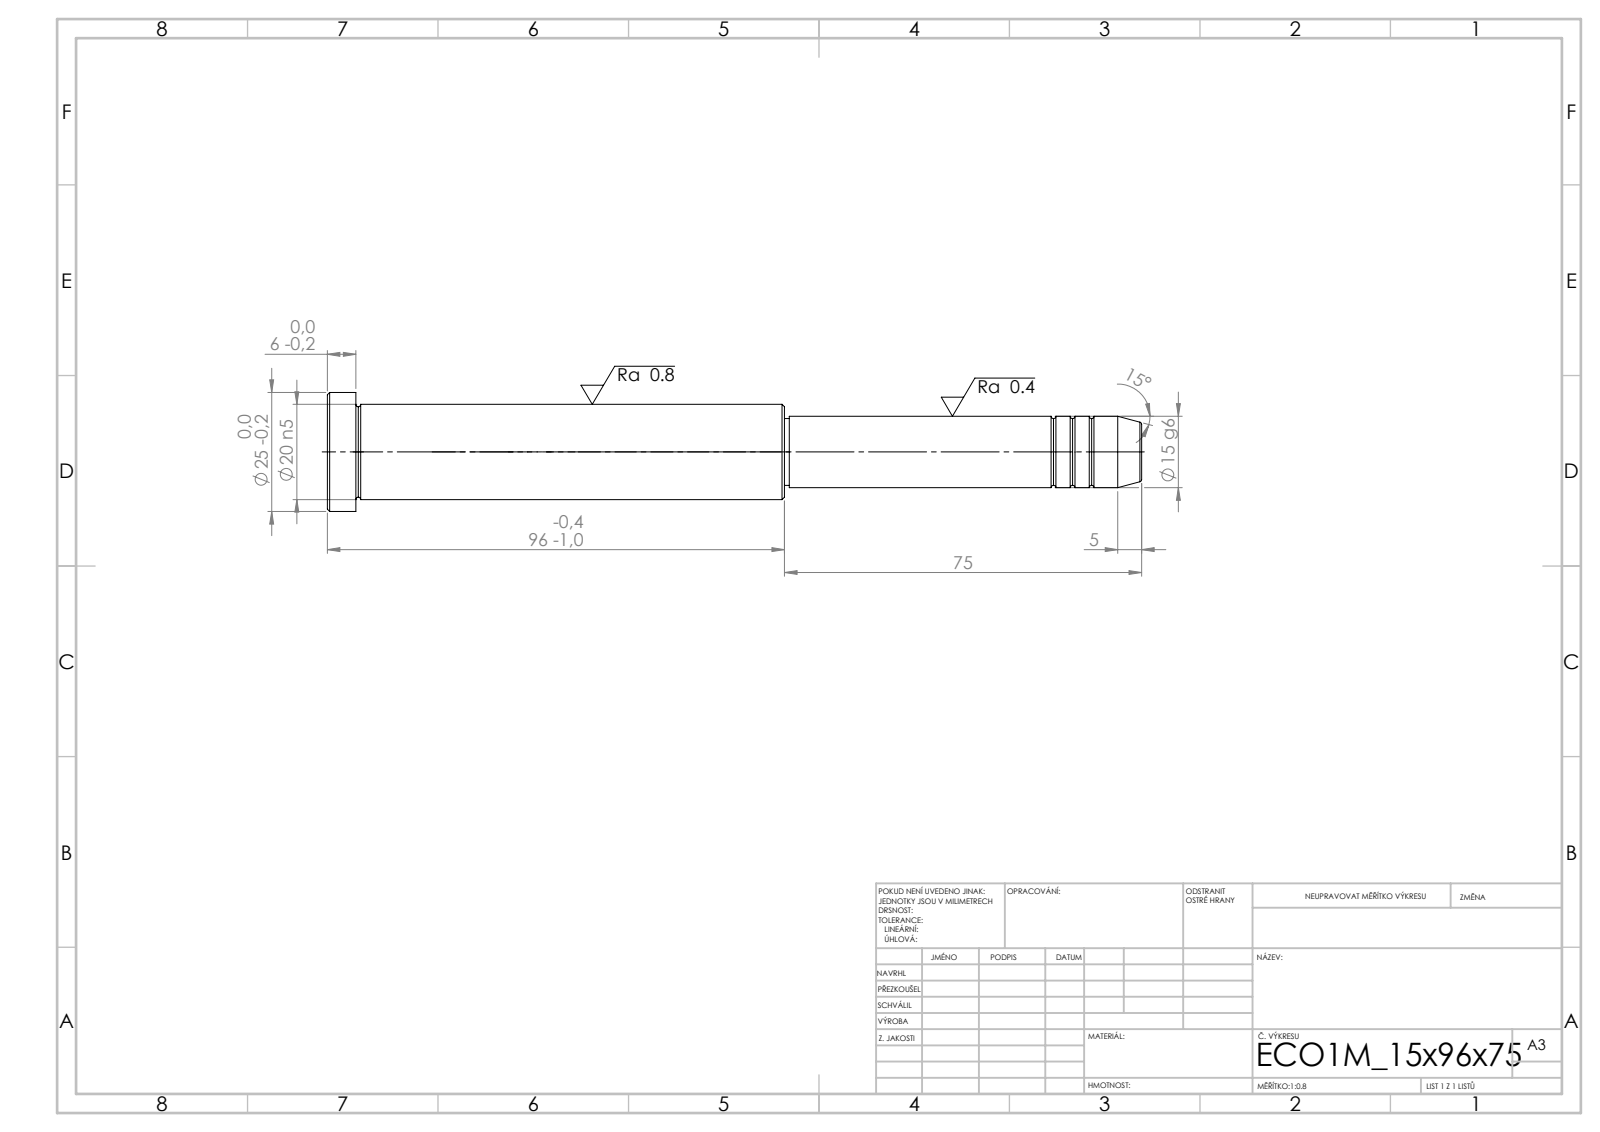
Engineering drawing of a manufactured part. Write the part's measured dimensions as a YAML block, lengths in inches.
step_written_by: "SolidWorks 2019 (CONFIG_CONTROL_DESIGN)"
units: inches
bodies: {solids: 1, faces: 43, planar: 5, cylindrical: 14, other: 24}
overall_size: [6.732, 0.984, 0.984]
volume: 2.698
surface_area: 16.54
round_bosses_or_shafts:
  - {diameter: 0.984, count: 1}
  - {diameter: 0.787, count: 1}
  - {diameter: 0.591, count: 1}
  - {diameter: 0.551, count: 1}
face_to_face_distances: [0.236, 3.543, 3.78, 2.953, 6.496, 6.732, 2.913, 0.039, 3.583, 3.819]
